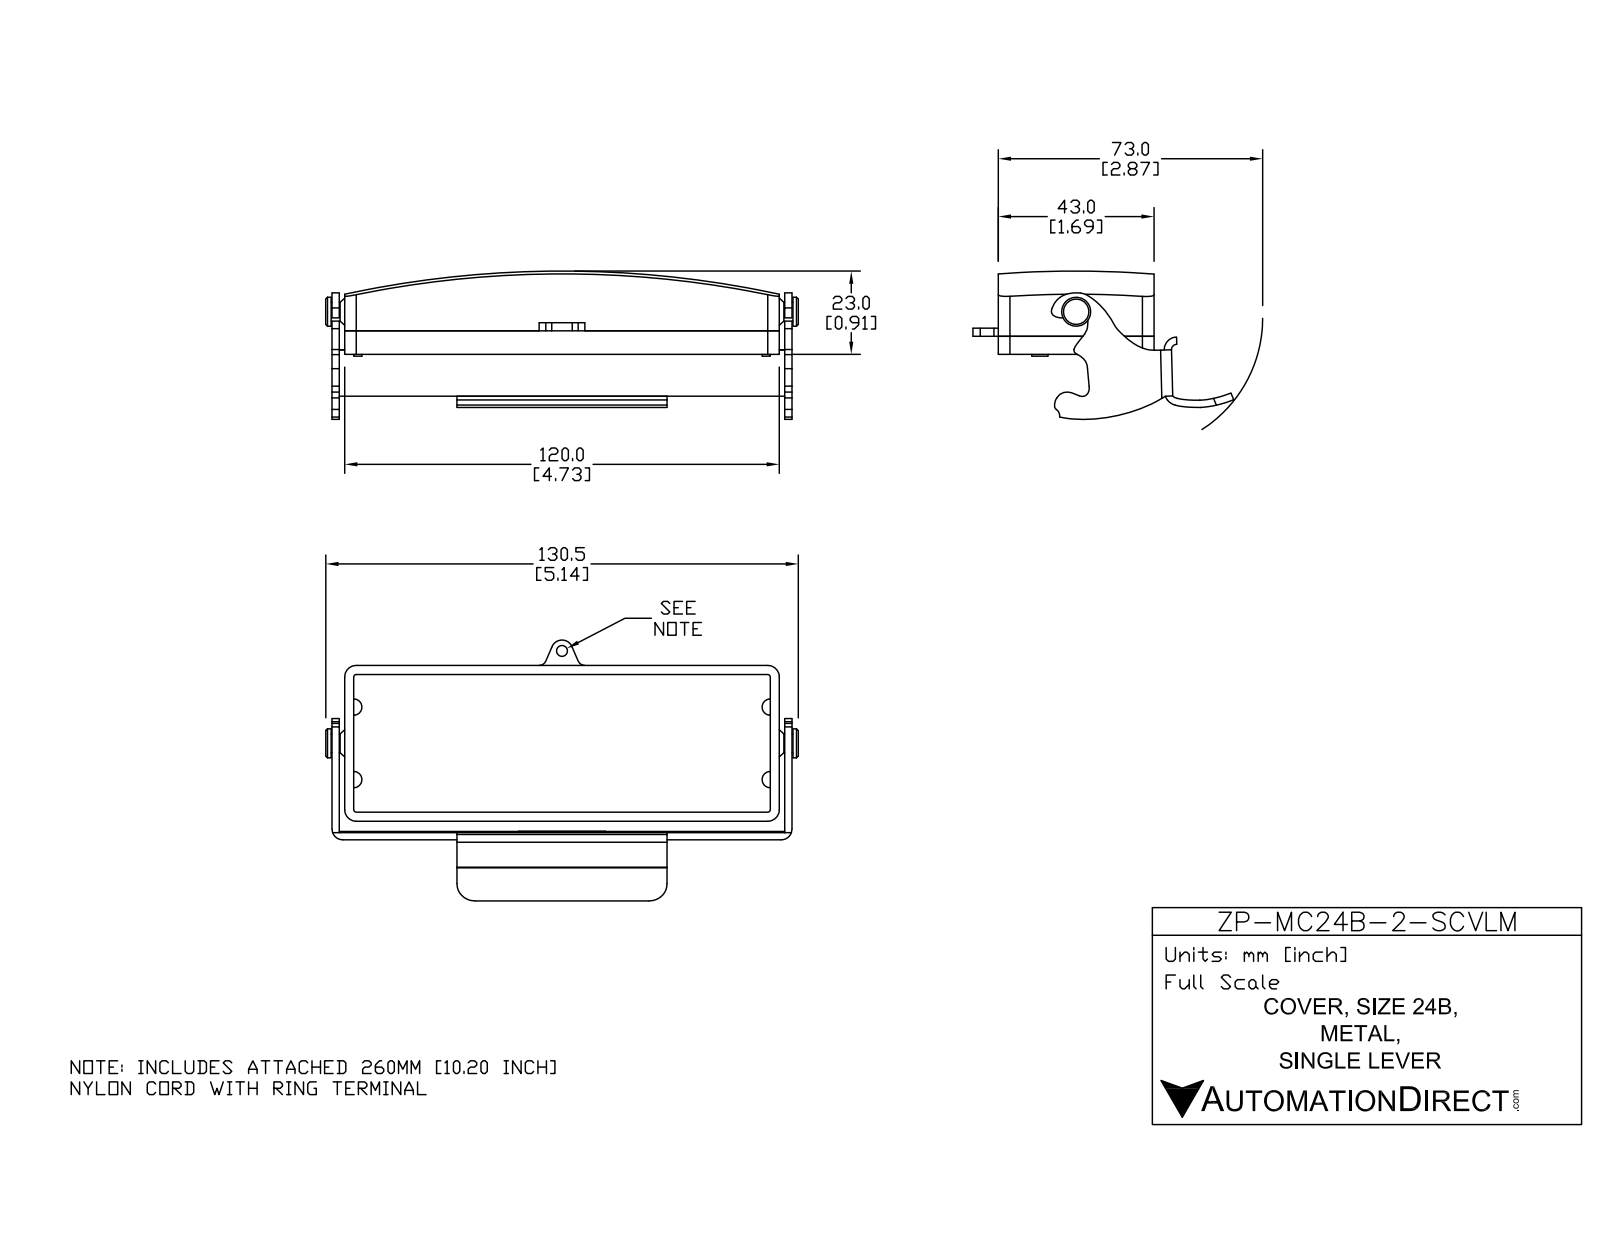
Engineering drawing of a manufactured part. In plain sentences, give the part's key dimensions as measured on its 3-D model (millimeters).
The part is named "ZP-MC24B-2-SCVLM". Its 3-D file was written by "SolidWorks 2011 (AUTOMOTIVE_DESIGN)". It is 5 solids with 164 faces: 70 planar, 88 cylindrical and 6 other. Overall it measures 130.5 by 76.22 by 37.55 millimeters. Its volume is 29 945 cubic millimeters and its surface area 31 065 square millimeters. Round holes: 1 of diameter 3. Round bosses or shafts: 1 of diameter 8, 1 of diameter 5.17. Partial cylindrical surfaces (rounded edges, fillets, slot ends): 13 of radius 0.5, 5 of radius 2, 4 of radius 0.7, 4 of radius 2.25, 4 of radius 3.2, 3 of radius 4, 2 of radius 1, 2 of radius 3. The main face-to-face distances are 2.5, 40.5, 1.15, 43, 38, 121.25, 2.4, 122.4, 123.65, 1.25.
